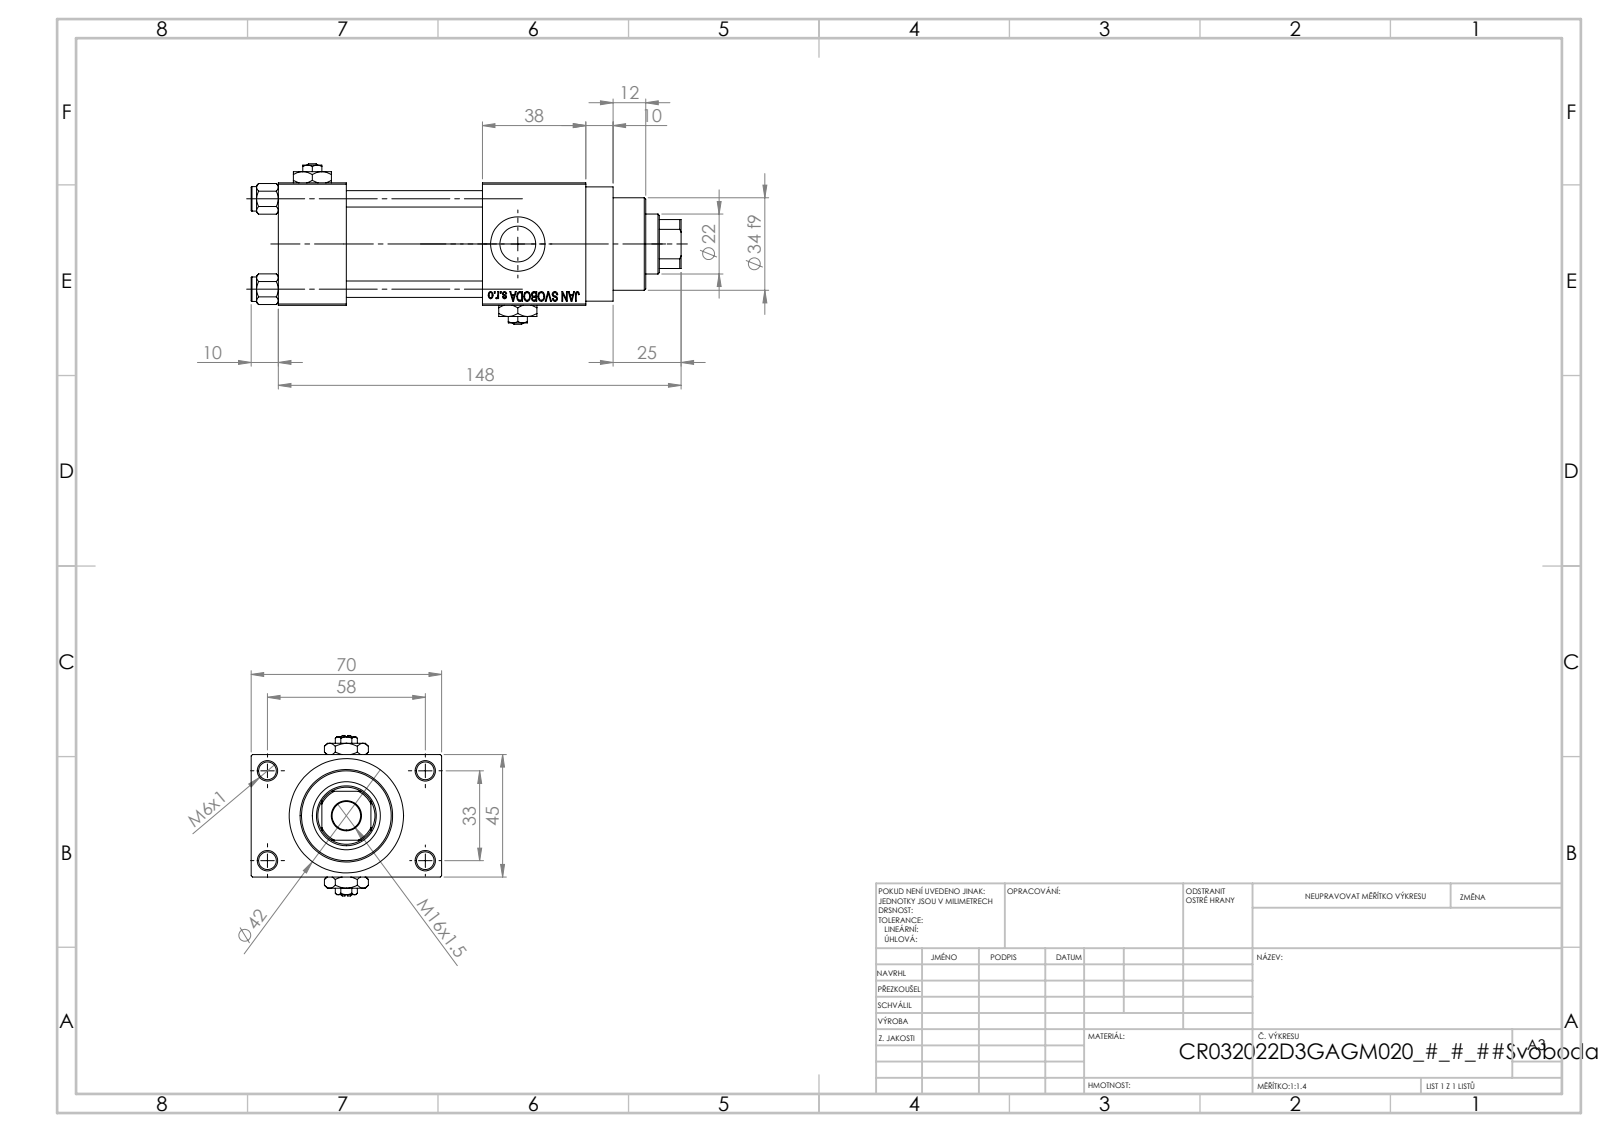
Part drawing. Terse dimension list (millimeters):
name: V215CR_D_TYCINKA; NUT_M5_D; Zatka_pro_OIL_PORT; V215_VC_A (+2 more)
written by: SolidWorks 2019 (CONFIG_CONTROL_DESIGN)
unit: mm
bodies: 13 solids, 1192 faces (541 planar, 93 cylindrical, 558 other)
size: 158 × 70 × 59
volume: 243 658 mm³; area: 81 170 mm²
holes: 4× ⌀6, 4× ⌀6.5, 3× ⌀13.16, 3× ⌀20, 2× ⌀7, 1× ⌀10.5, 1× ⌀22, 1× ⌀24, 1× ⌀25, 1× ⌀32, 1× ⌀33
bosses: 4× ⌀9, 1× ⌀42, 1× ⌀38, 1× ⌀34
rounds: 1× R10.5
face distances: 45, 25, 12.5, 57.5, 50, 75, 88, 38, 113, 70
hole spacings: 12.4, 23.48, 33.2, 33.37, 35.35, 45.6, 56.35, 33
